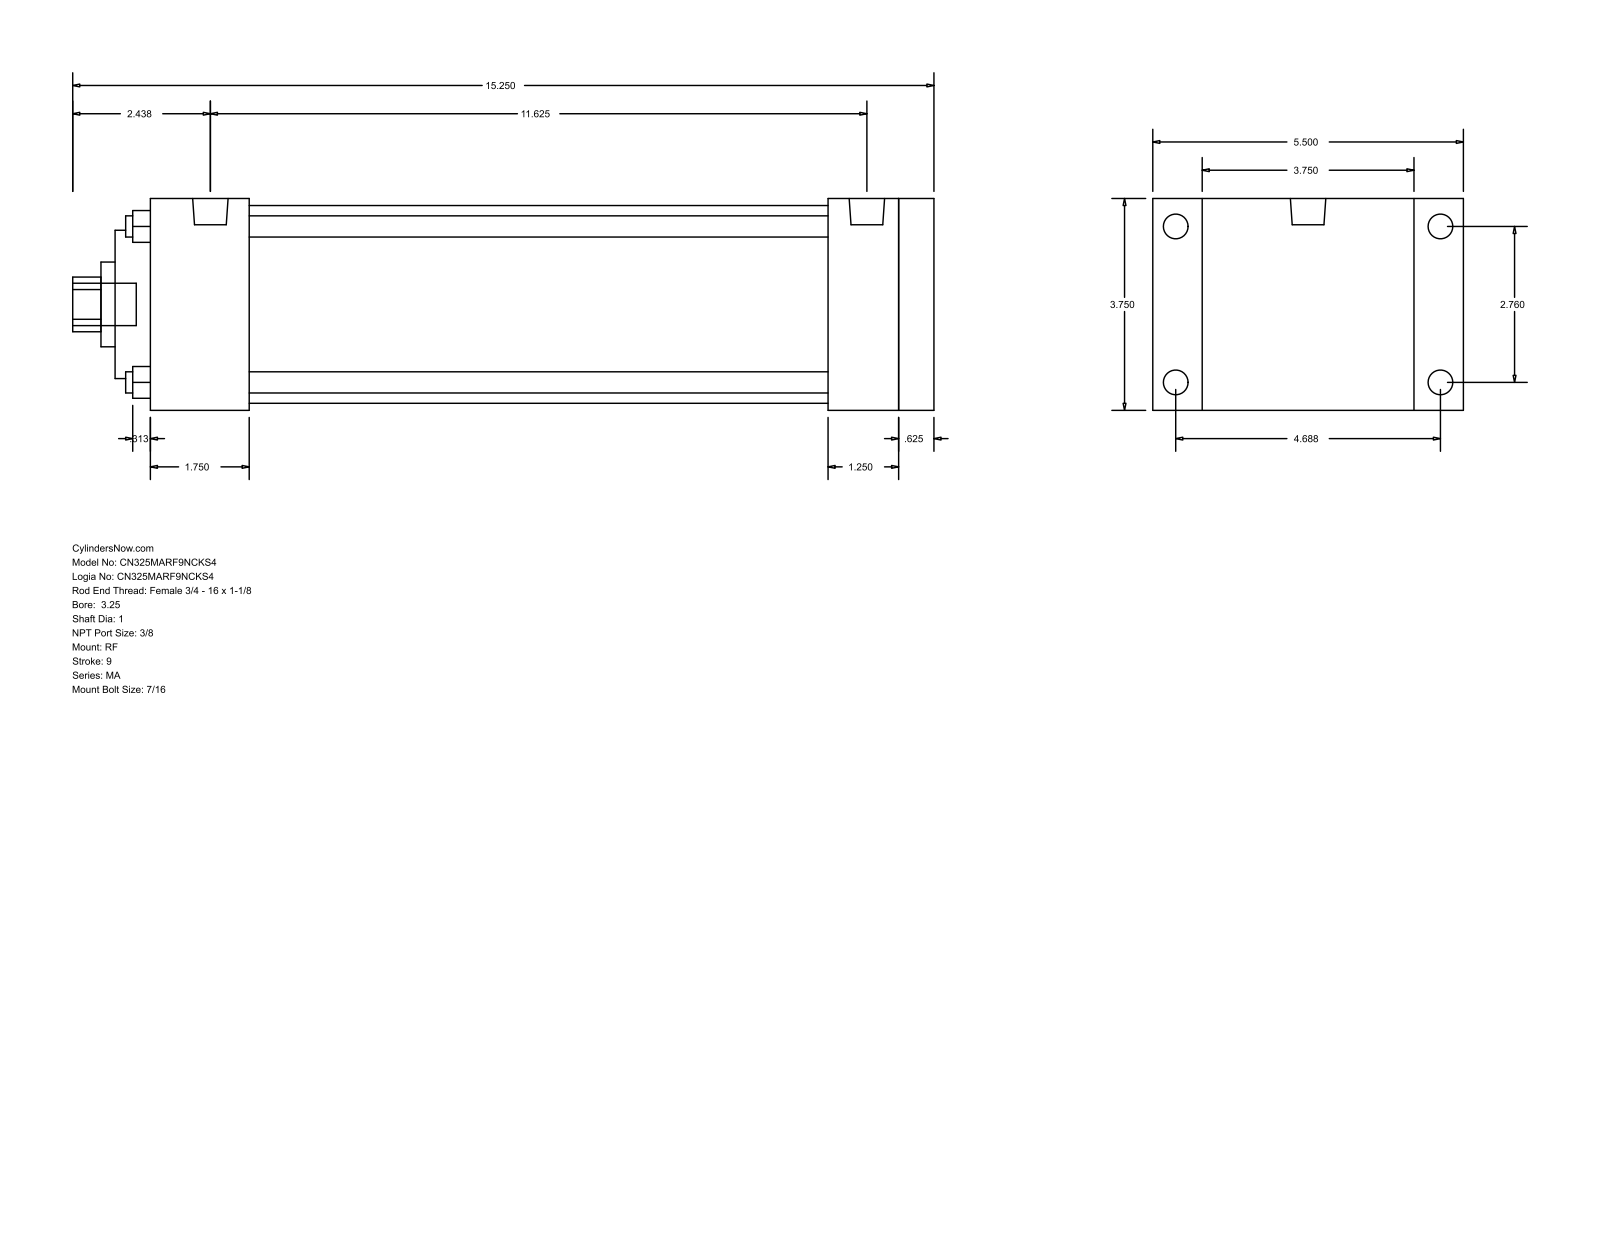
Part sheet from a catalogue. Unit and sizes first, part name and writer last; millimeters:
Units: millimetres
Overall size (bounding box): 387.35 × 139.7 × 95.25
Round holes (diameter × count): ⌀9.53 ×4, ⌀25.4 ×1, ⌀38.1 ×1, ⌀66.67 ×1, ⌀88.9 ×1
Round bosses / shafts (diameter × count): ⌀11.11 ×8, ⌀15.93 ×2, ⌀19.05 ×1
Partial cylindrical surfaces — rounded edges, fillets, slot ends (radius × count): R12.29 ×1
Main face-to-face distances: 95.24, 352.43, 15.87, 336.56, 22.23, 117.47, 304.81, 31.75, 47.62, 44.46
Hole centre spacings: 49.57, 70.1, 99.14
Bodies: 0 solids, 94 faces (65 planar, 29 cylindrical, 0 other)
Part name (STEP PRODUCT): MA_RF__0325_1
STEP written by: GSSL Pune (CONFIG_CONTROL_DESIGN)
